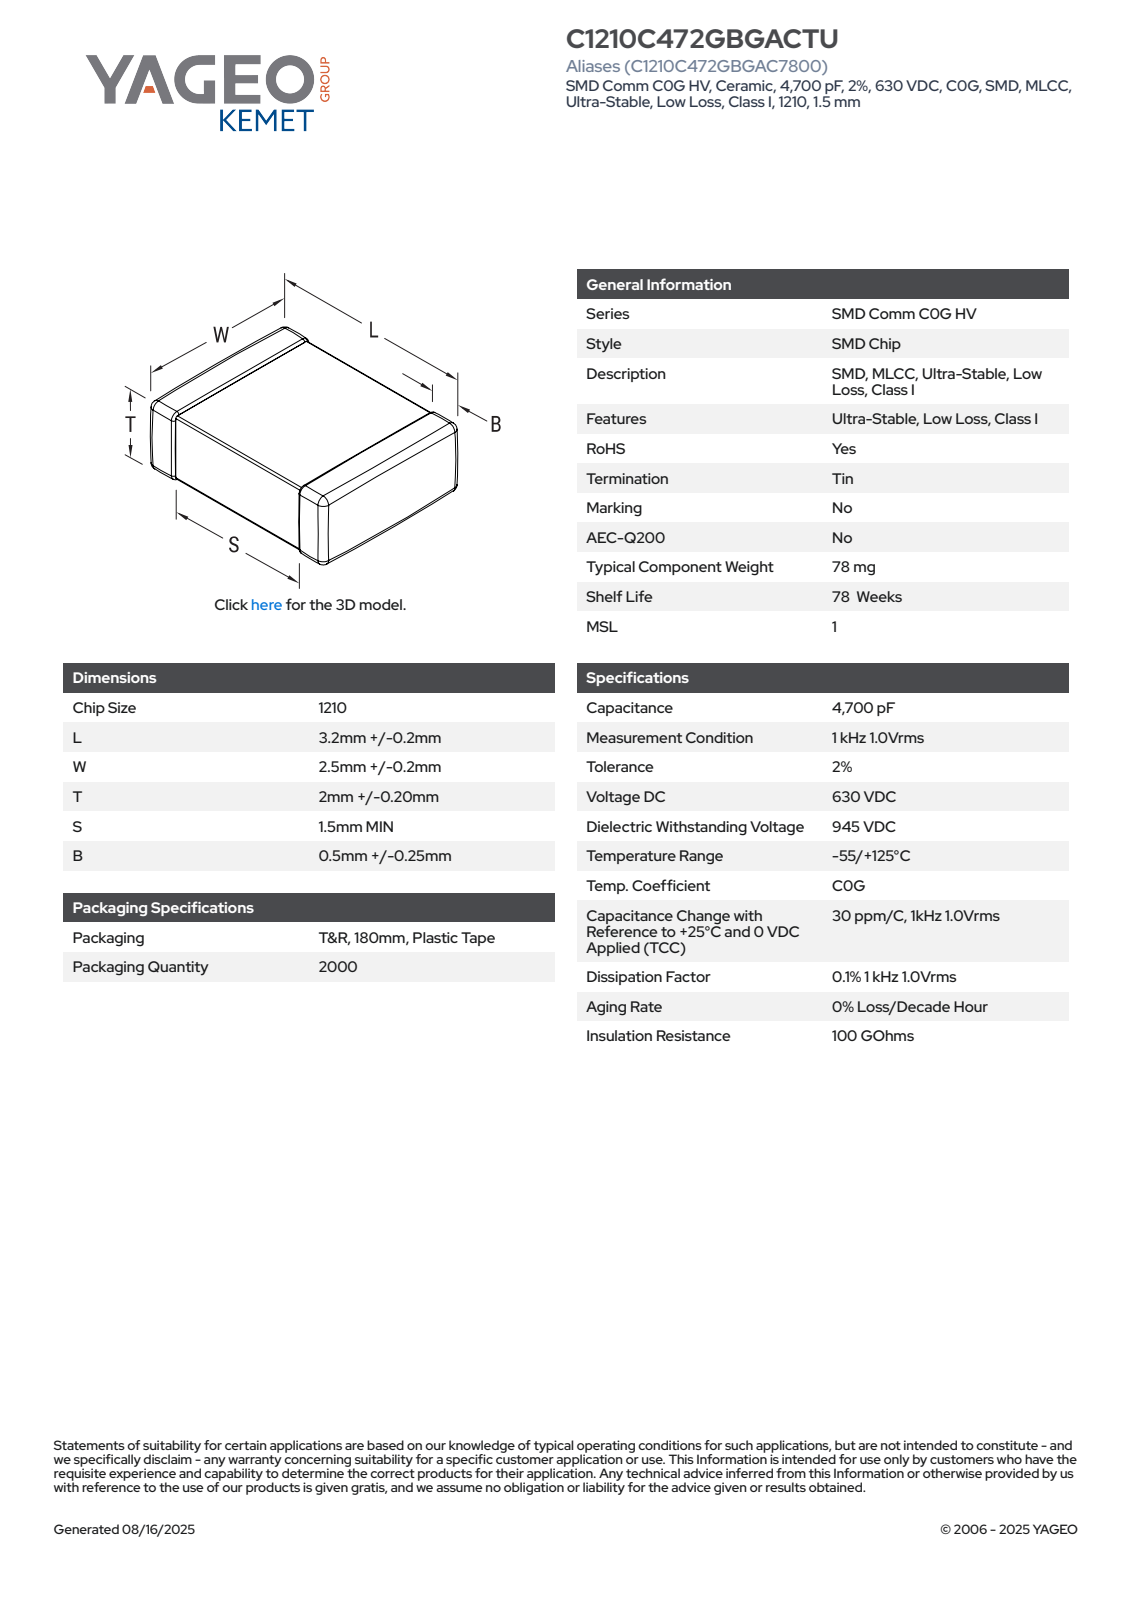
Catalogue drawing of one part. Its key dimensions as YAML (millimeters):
part_name: "CCS_CCSTDNOS_1210_L3.4W2.7T2.2B0.75"
step_written_by: "SolidWorks 2014 (AUTOMOTIVE_DESIGN)"
units: millimeters
bodies: {solids: 4, faces: 125, planar: 71, cylindrical: 38, other: 16}
overall_size: [3.4, 2.7, 2.2]
volume: 19
surface_area: 45
face_to_face_distances: [2.14, 3.4, 2.64, 2.08, 2.58, 2.2, 2.7, 2.15, 2.09, 1.31]
